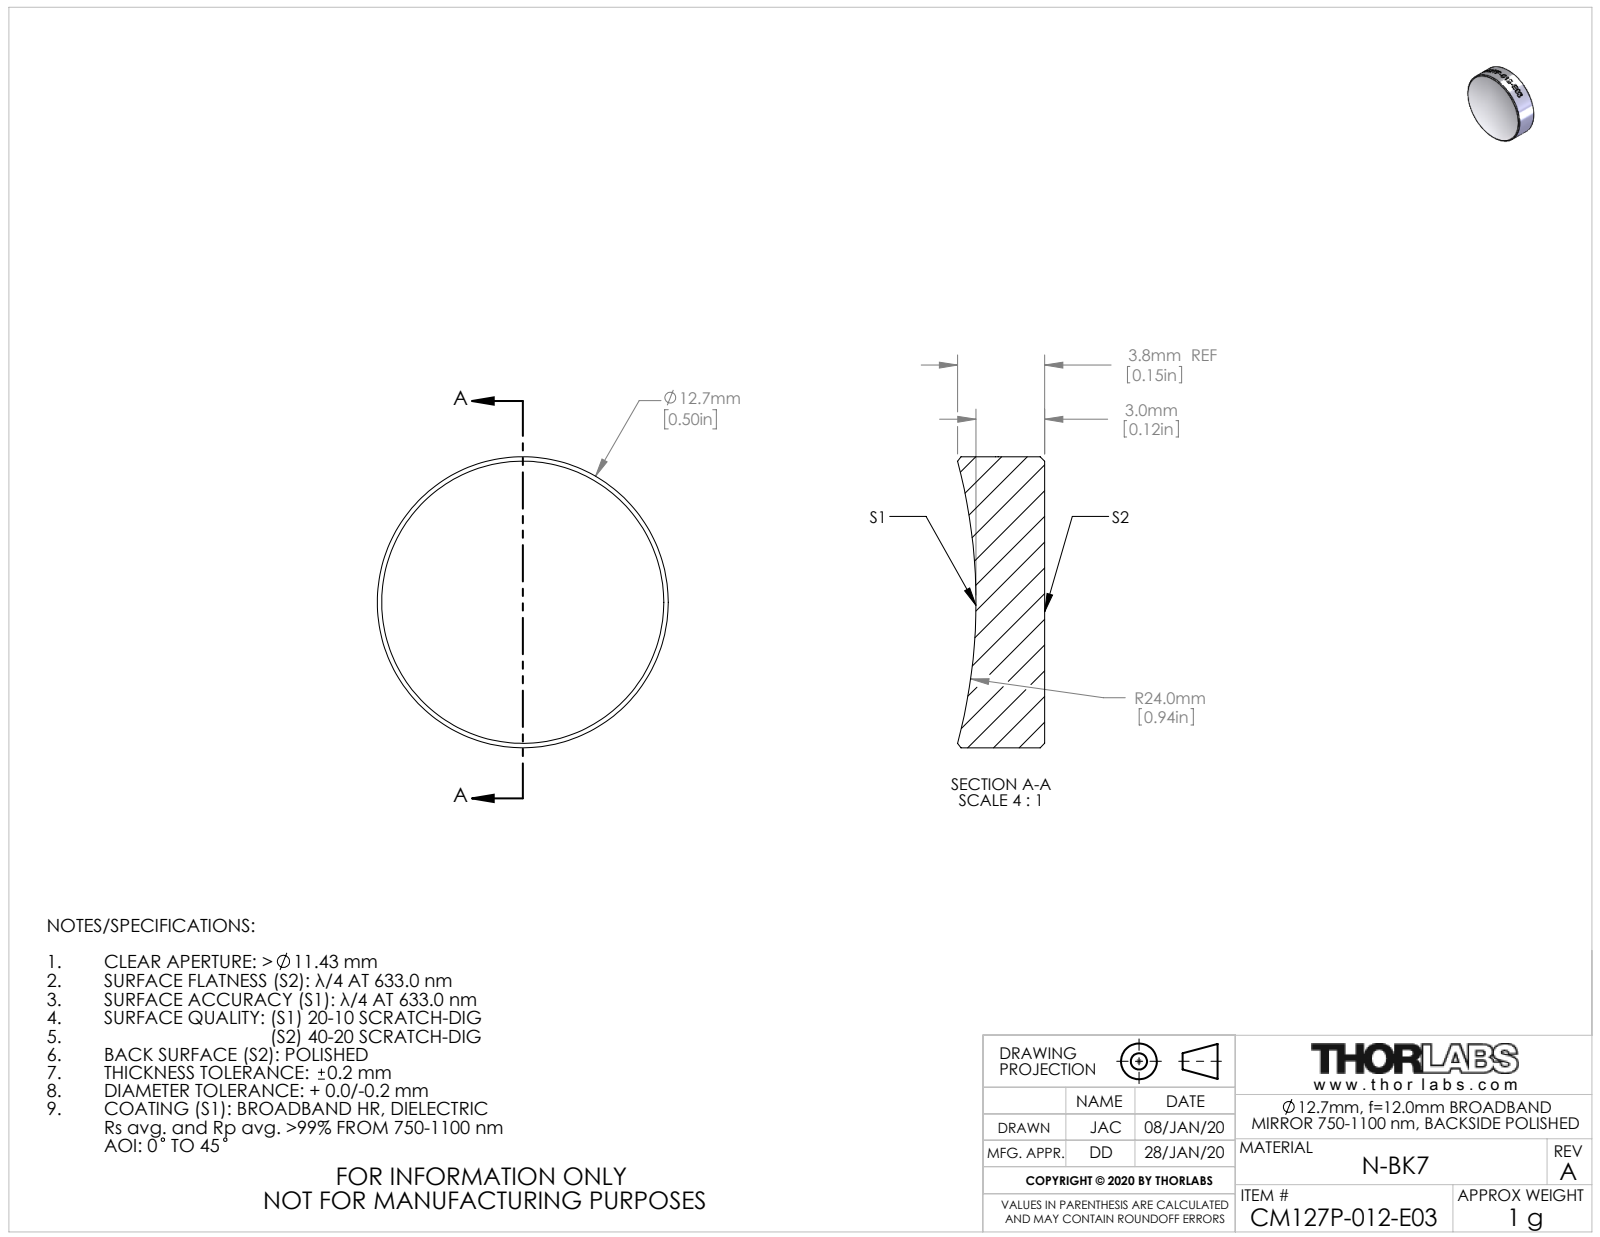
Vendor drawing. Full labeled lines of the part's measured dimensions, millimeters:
Part name (STEP PRODUCT): TTN201377-E0W
STEP written by: SolidWorks 2018 (CONFIG_CONTROL_DESIGN)
Units: millimetres
Bodies: 1 solid, 26 faces (1 planar, 19 cylindrical, 6 other)
Overall size (bounding box): 12.7 × 12.7 × 3.8
Volume: 432 mm³ · Surface area: 398 mm²
Round bosses / shafts (diameter × count): ⌀12.7 ×1
